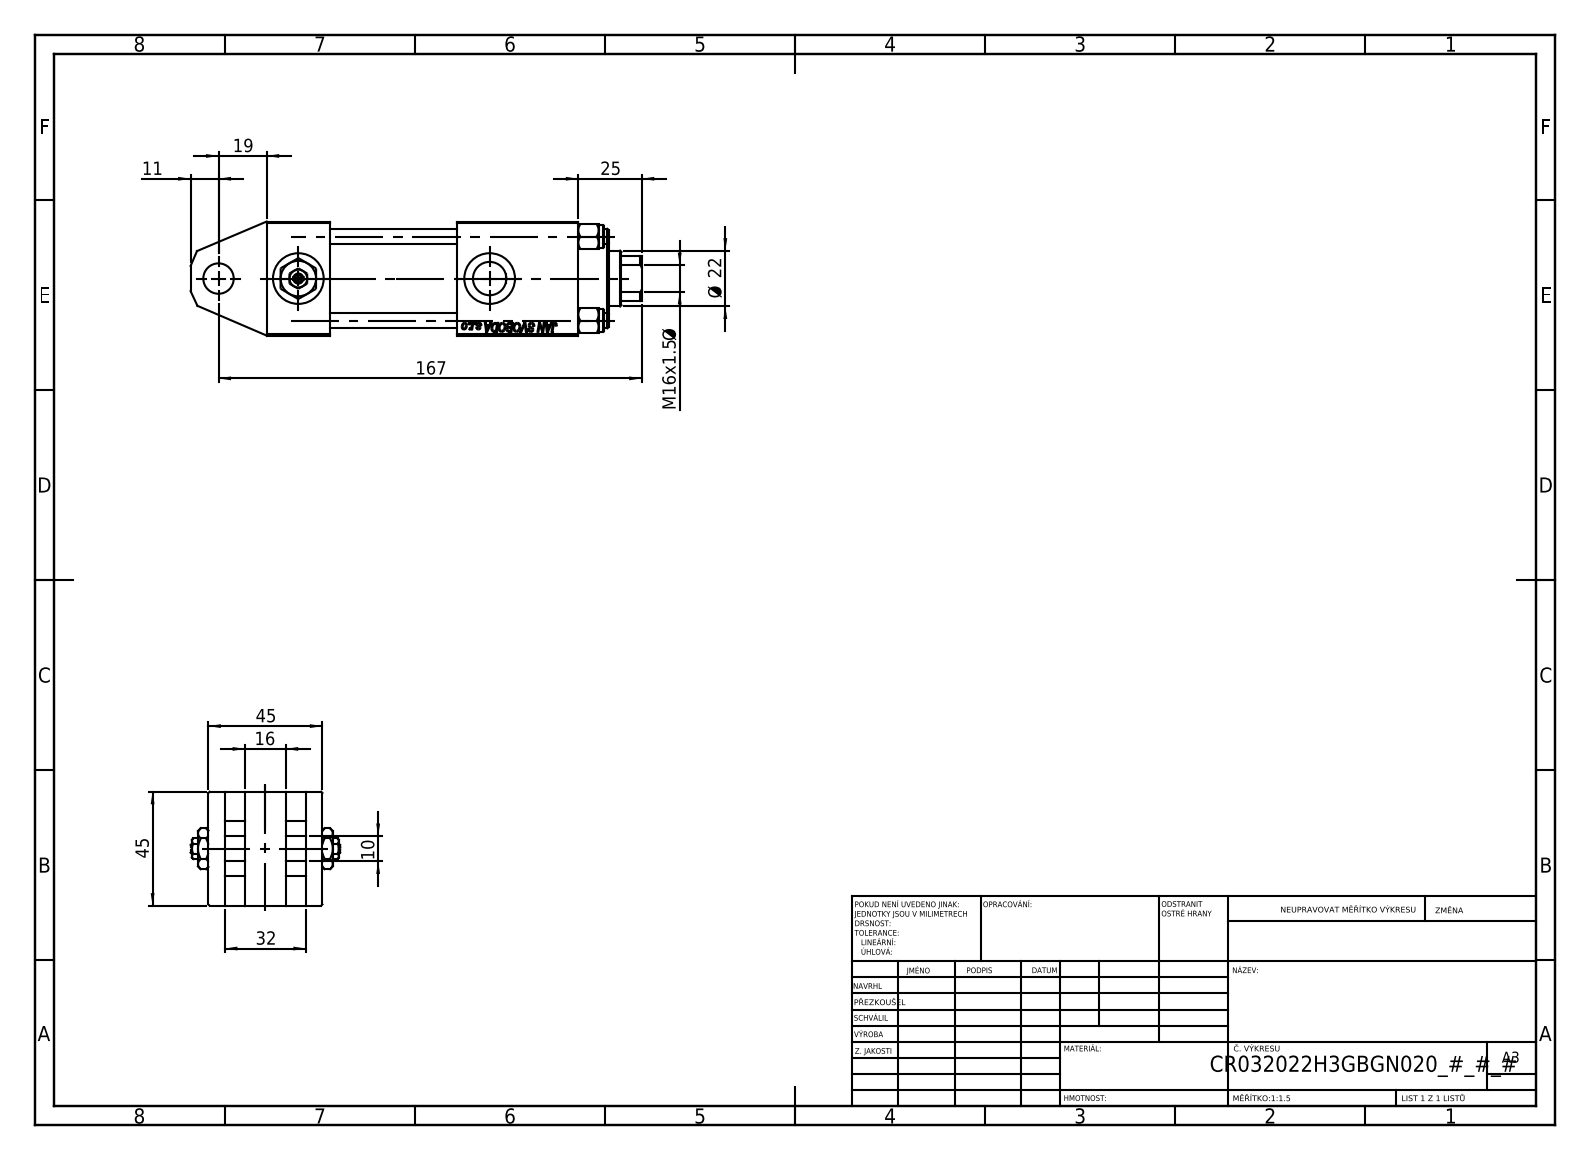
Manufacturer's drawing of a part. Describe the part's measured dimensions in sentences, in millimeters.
The part is named "V215CR_H_Body; V215CR_TYCINKA_H; V215_VC_A; Zatka_pro_OIL_PORT (+2 more)". Its 3-D file was written by "SolidWorks 2019 (CONFIG_CONTROL_DESIGN)". It is 13 solids with 1228 faces: 564 planar, 94 cylindrical and 570 other. Overall it measures 178 by 59 by 45 millimeters. Its volume is 223 282 cubic millimeters and its surface area 80 264 square millimeters. Round holes: 4 of diameter 6, 2 of diameter 7, 2 of diameter 13.16, 2 of diameter 20, 1 of diameter 10.5, 1 of diameter 12, 1 of diameter 22, 1 of diameter 24, 1 of diameter 25, 1 of diameter 32, 1 of diameter 33. Round bosses or shafts: 4 of diameter 9, 1 of diameter 38, 1 of diameter 34. Partial cylindrical surfaces (rounded edges, fillets, slot ends): 1 of radius 10.5. The main face-to-face distances are 45, 8, 6.5, 38.5, 14.5, 30.5, 24, 25, 123, 50. The hole center spacings are 23.48, 33.2, 46.95, 31.5, 75.5, 107.
